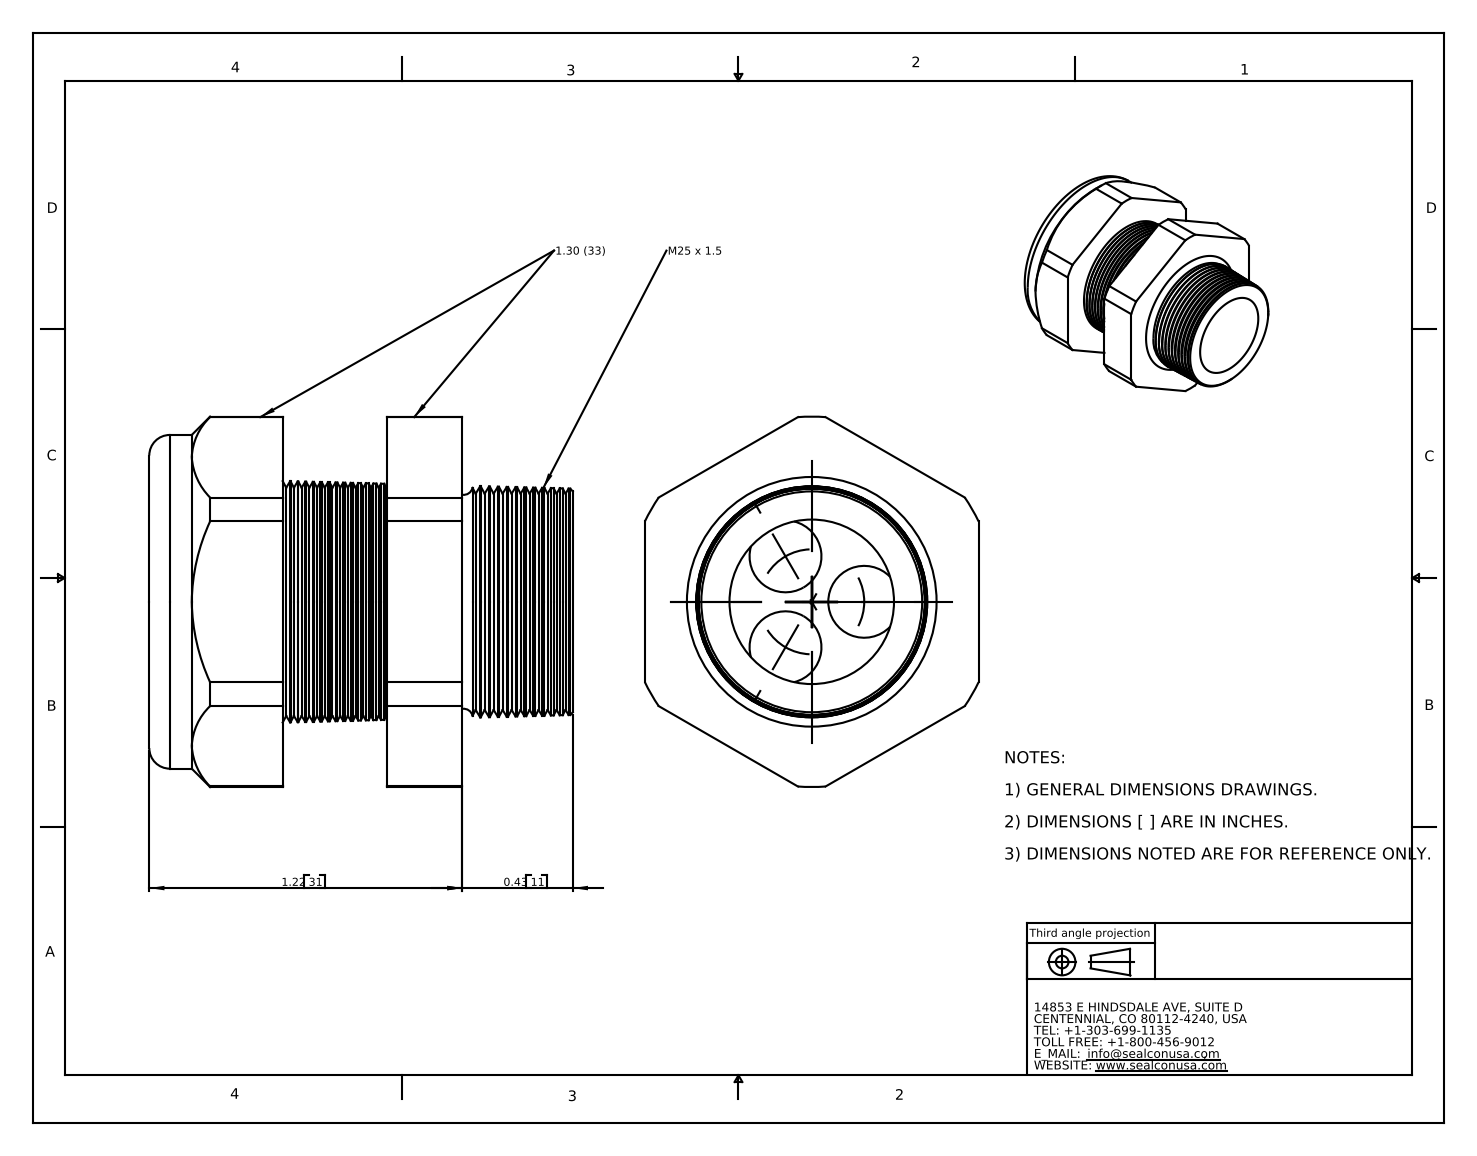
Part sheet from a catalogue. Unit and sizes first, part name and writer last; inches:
Units: inches
Overall size (bounding box): 1.65 × 1.443 × 1.3
Round holes (diameter × count): ⌀0.28 ×3, ⌀0.69 ×1, ⌀0.71 ×1
Round bosses / shafts (diameter × count): ⌀1.3 ×1
Partial cylindrical surfaces — rounded edges, fillets, slot ends (radius × count): R0.721 ×1
Main face-to-face distances: 1.3, 0.405, 0.7, 0.295, 0.52, 0.925, 1.22, 1.65, 1.13, 0.725
Hole centre spacings: 0.354, 0.205, 0.204
Volume: 1.13 in³ · Surface area: 17.06 in²
Bodies: 2 solids, 212 faces (20 planar, 26 cylindrical, 166 other)
Part name (STEP PRODUCT): CD25M2-BK
STEP written by: SolidWorks 2007 (CONFIG_CONTROL_DESIGN)
